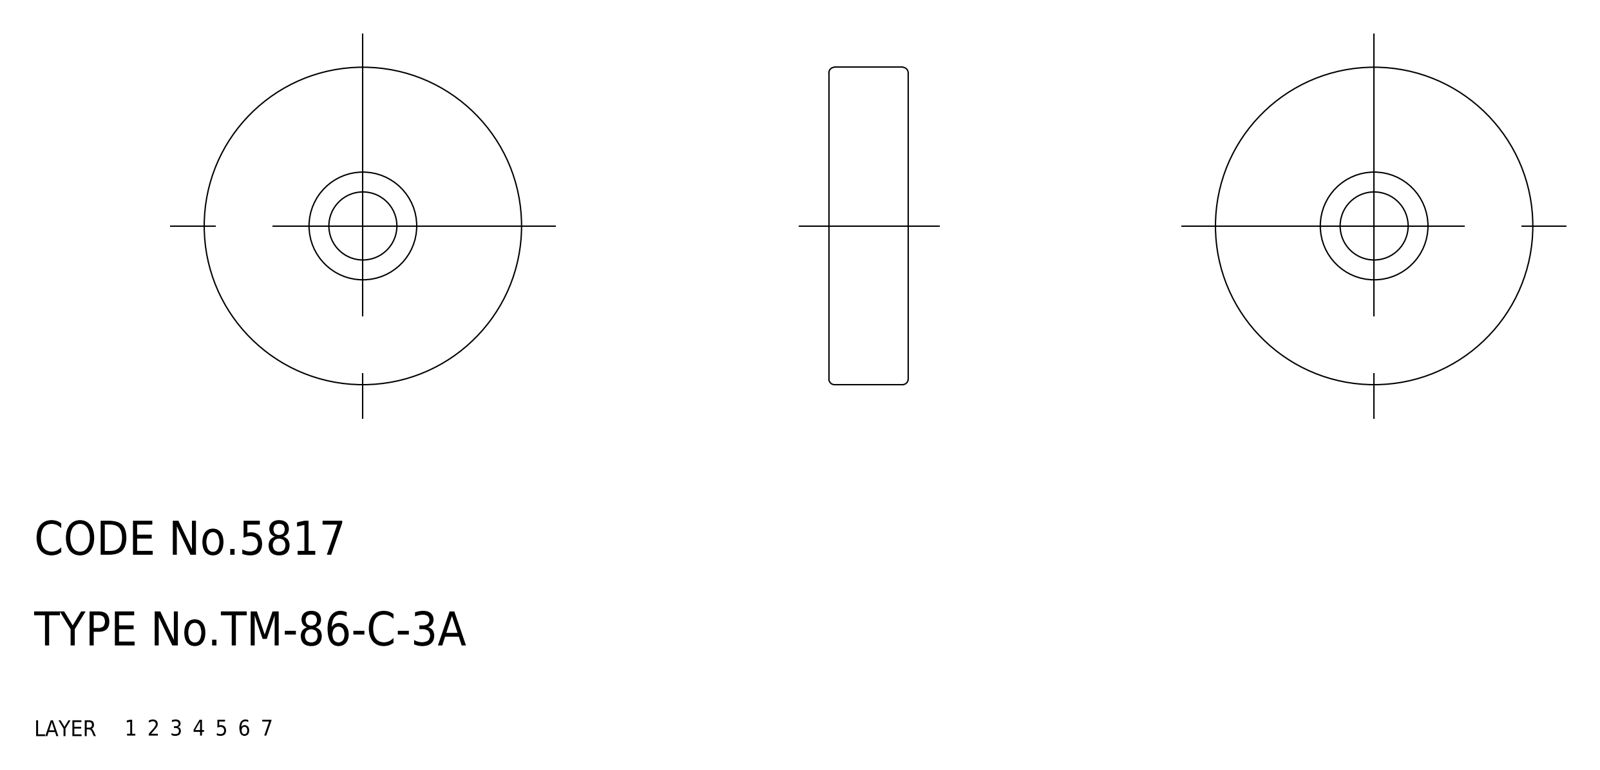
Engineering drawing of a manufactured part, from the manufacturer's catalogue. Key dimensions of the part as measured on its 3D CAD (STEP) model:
Part name (STEP PRODUCT): roller
STEP written by: CADfix (AUTOMOTIVE_DESIGN)
Units: millimetres
Bodies: 1 solid, 28 faces (0 planar, 0 cylindrical, 28 other)
Overall size (bounding box): 28 × 28 × 7
Volume: 4 104 mm³ · Surface area: 2 399 mm²
